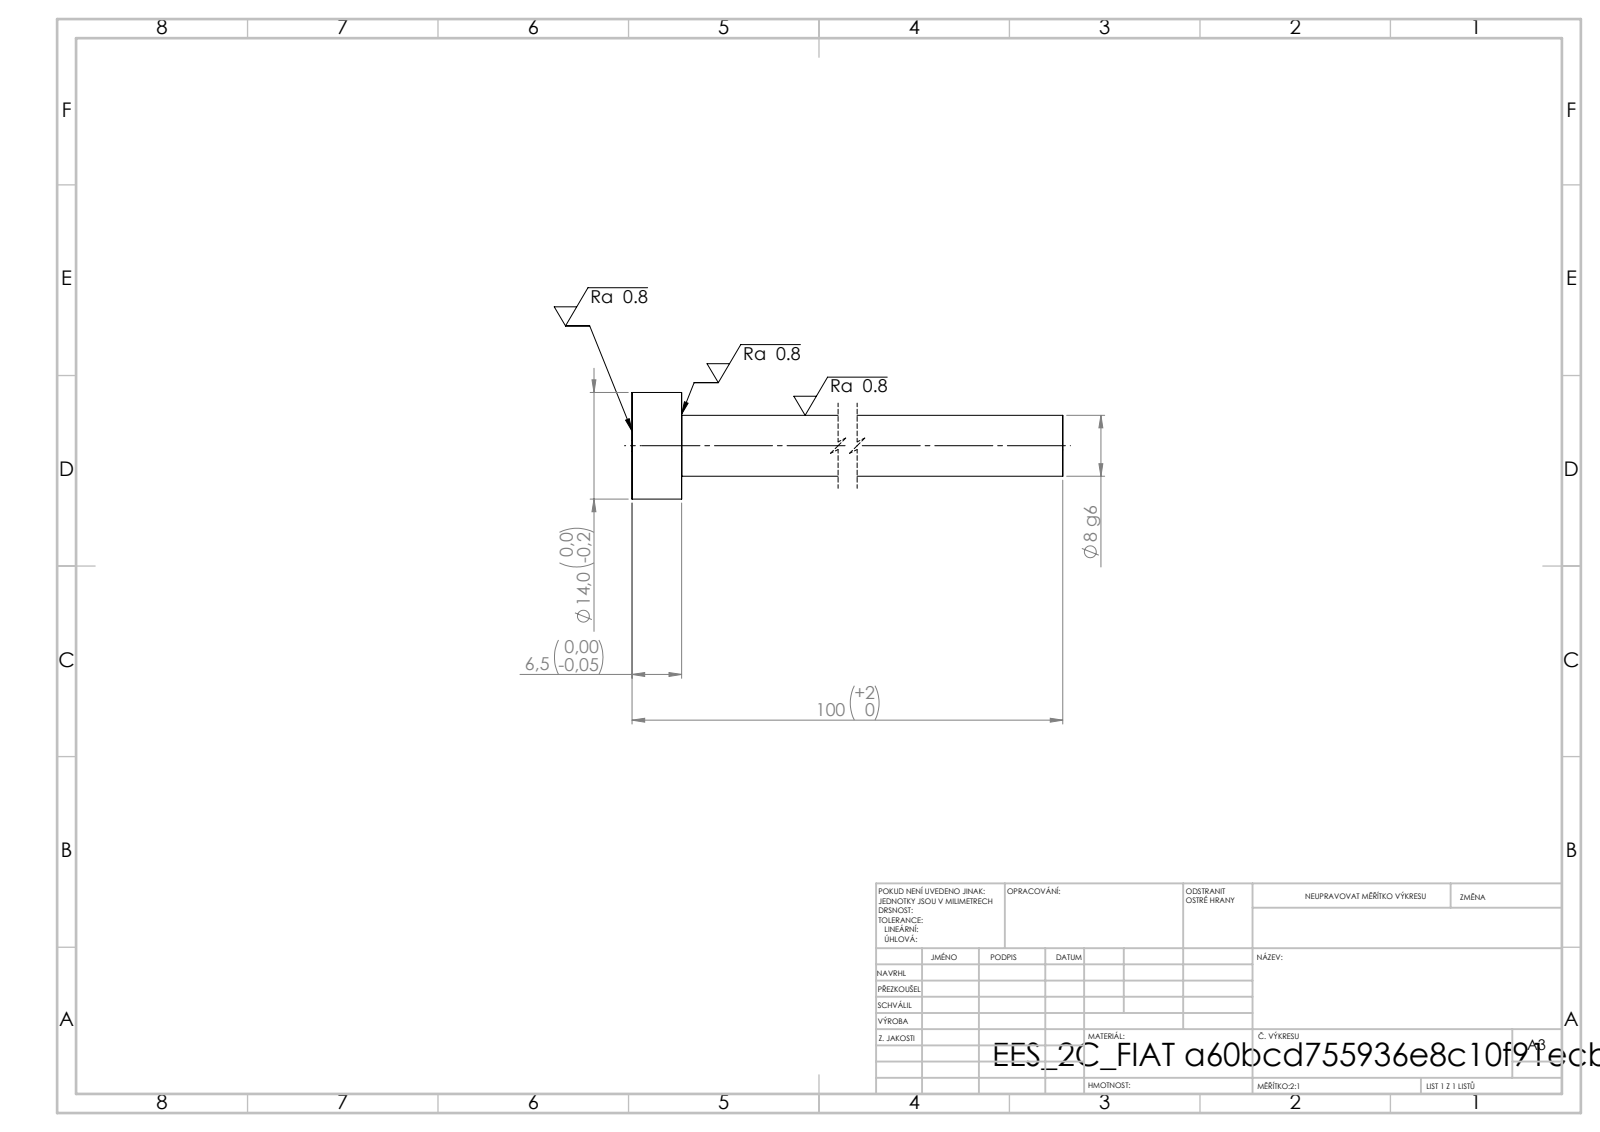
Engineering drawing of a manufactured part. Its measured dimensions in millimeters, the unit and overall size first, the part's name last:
Units: millimetres
Overall size (bounding box): 100 × 14 × 14
Round bosses / shafts (diameter × count): ⌀14 ×1, ⌀8 ×1
Main face-to-face distances: 6.5, 100, 93.5
Volume: 5 700 mm³ · Surface area: 2 944 mm²
Bodies: 1 solid, 7 faces (3 planar, 4 cylindrical, 0 other)
STEP written by: SolidWorks 2019 (CONFIG_CONTROL_DESIGN)
